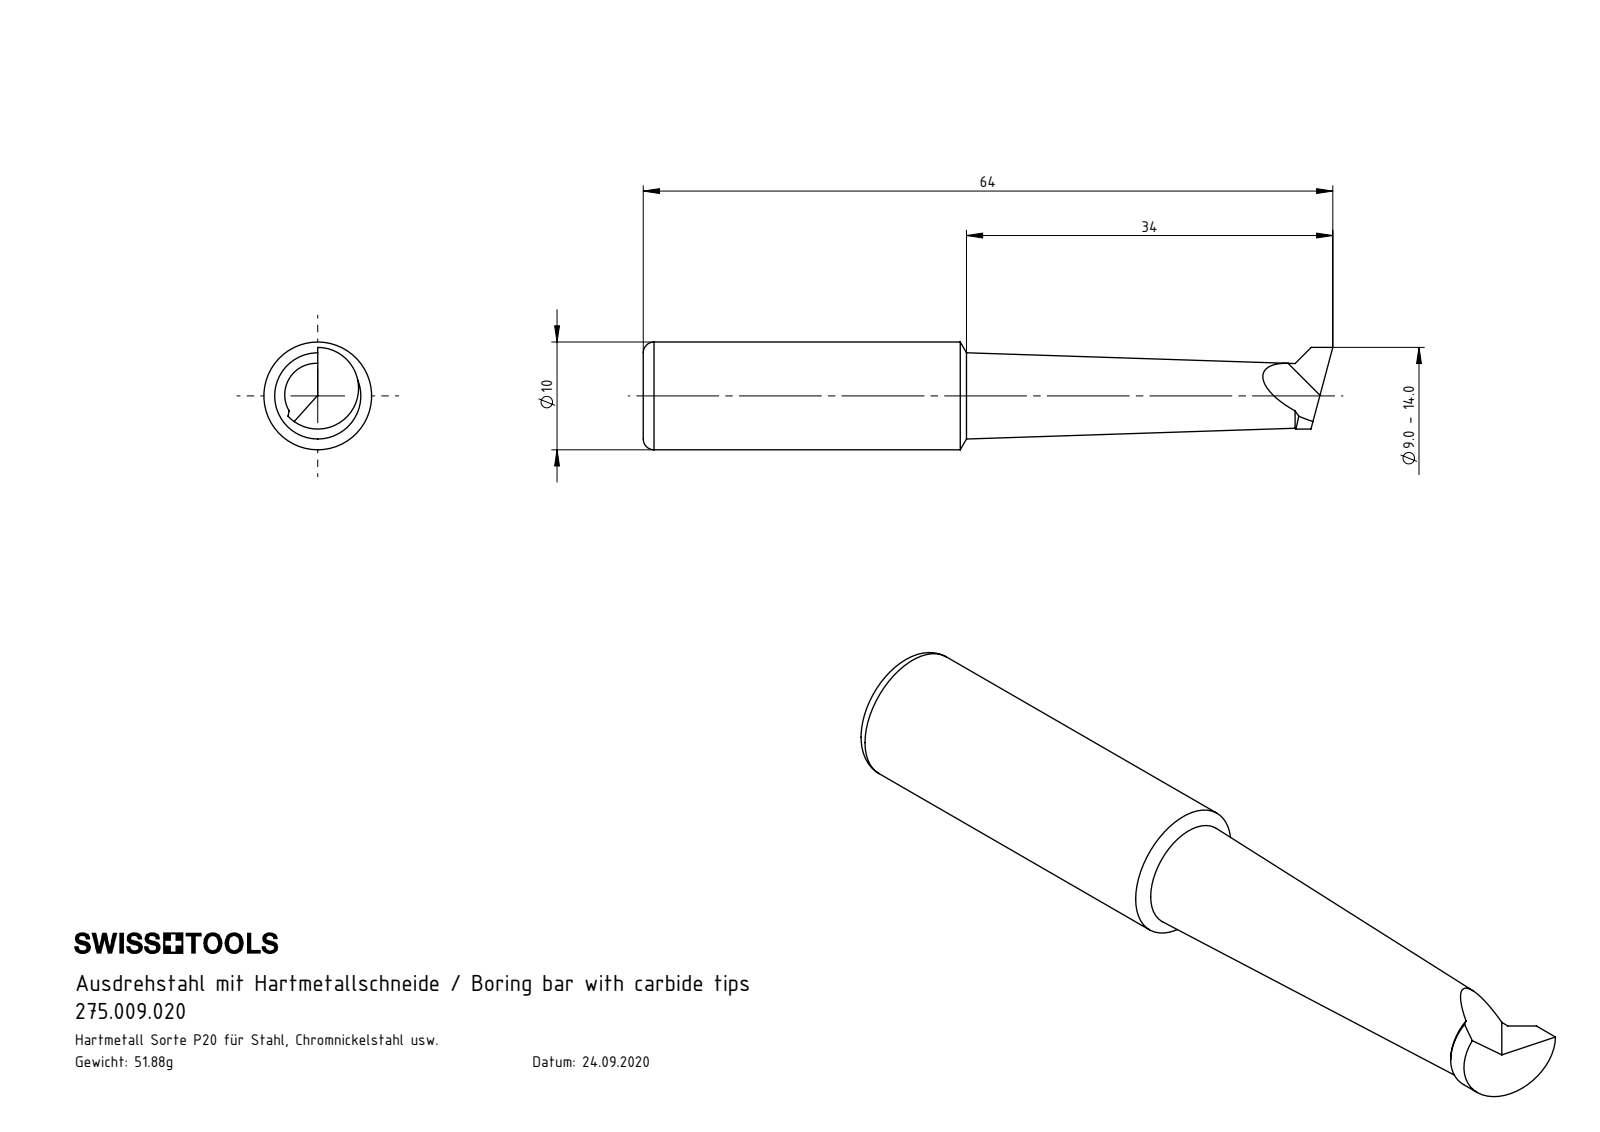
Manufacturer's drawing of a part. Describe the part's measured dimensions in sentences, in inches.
The part is named "275.009.020". Its 3-D file was written by "SolidWorks 2022 (CONFIG_CONTROL_DESIGN)". It is 1 solid with 14 faces: 4 planar, 3 cylindrical and 7 other. Overall it measures 2.52 by 0.394 by 0.394 inches. Its volume is 0.218 cubic inches and its surface area 2.753 square inches. Round bosses or shafts: 1 of diameter 0.394. Partial cylindrical surfaces (rounded edges, fillets, slot ends): 1 of radius 0.149.
